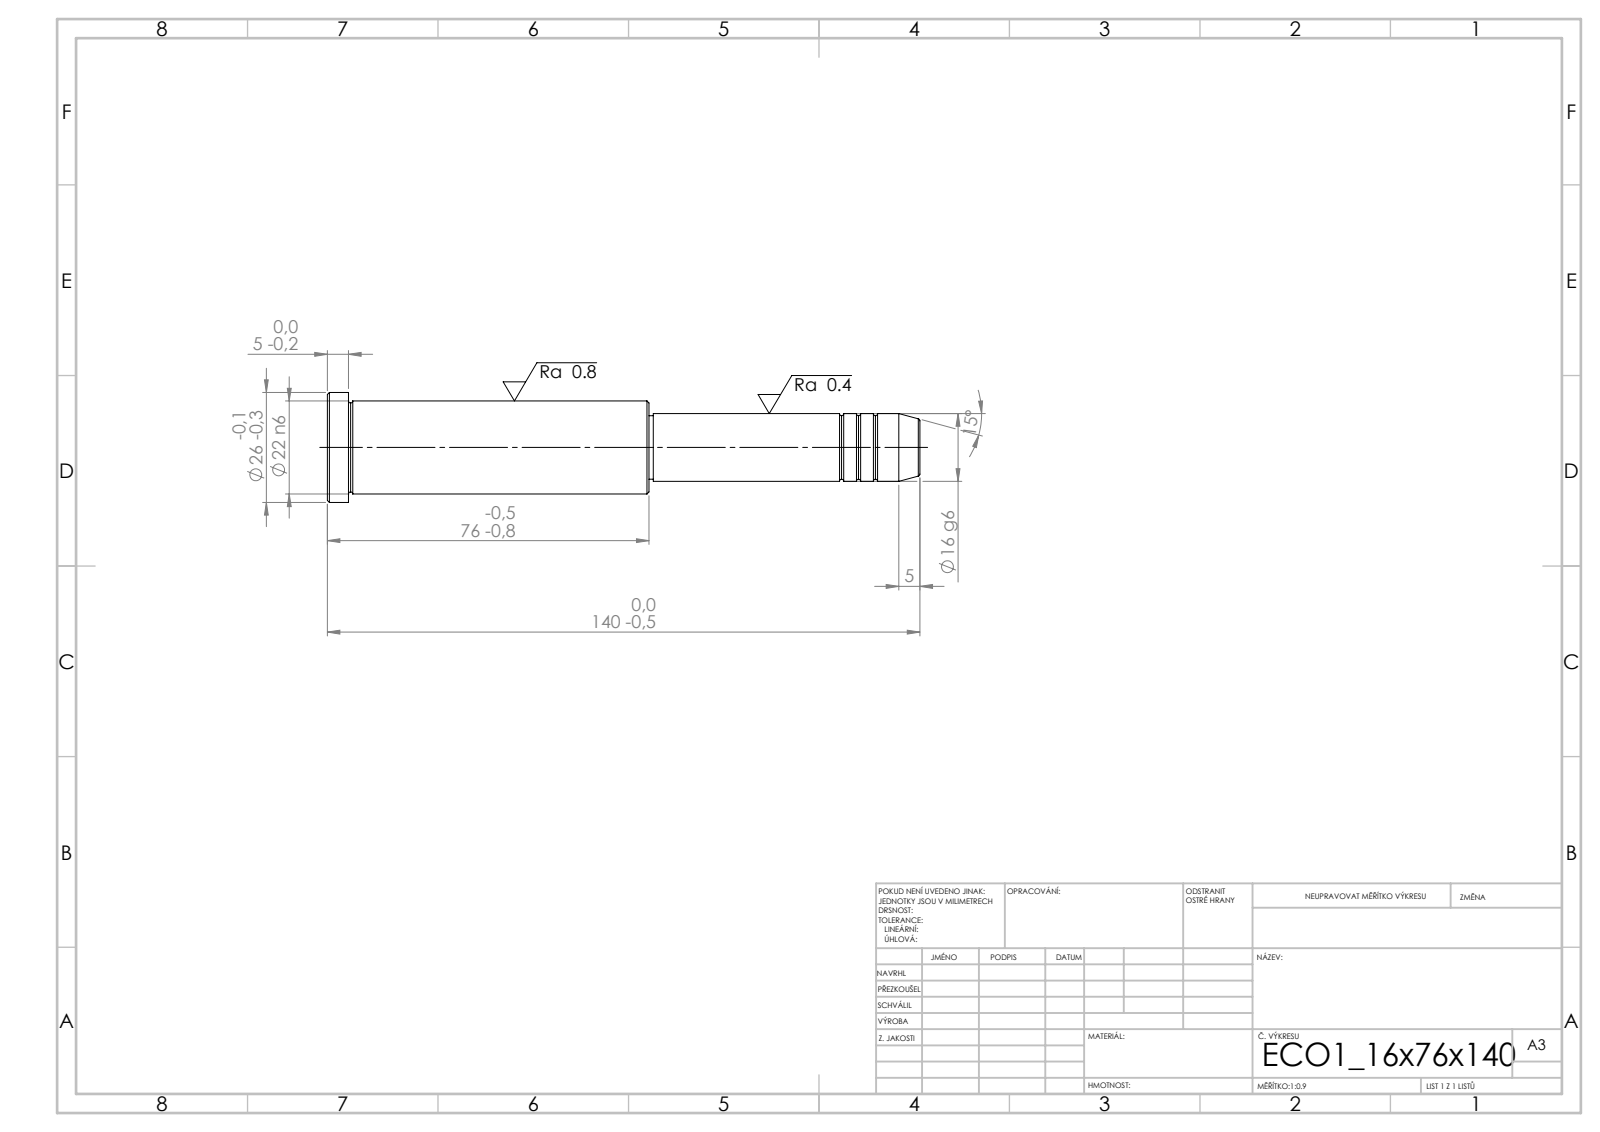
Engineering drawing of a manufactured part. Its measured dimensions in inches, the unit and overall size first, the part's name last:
Units: inches
Overall size (bounding box): 5.512 × 1.024 × 1.024
Round bosses / shafts (diameter × count): ⌀1.024 ×1, ⌀0.866 ×1, ⌀0.63 ×1, ⌀0.591 ×1
Main face-to-face distances: 2.992, 2.795, 0.197, 2.52, 5.315, 5.512, 2.48, 0.039, 2.835, 3.031
Volume: 2.577 in³ · Surface area: 14.92 in²
Bodies: 1 solid, 43 faces (5 planar, 14 cylindrical, 24 other)
STEP written by: SolidWorks 2019 (CONFIG_CONTROL_DESIGN)
